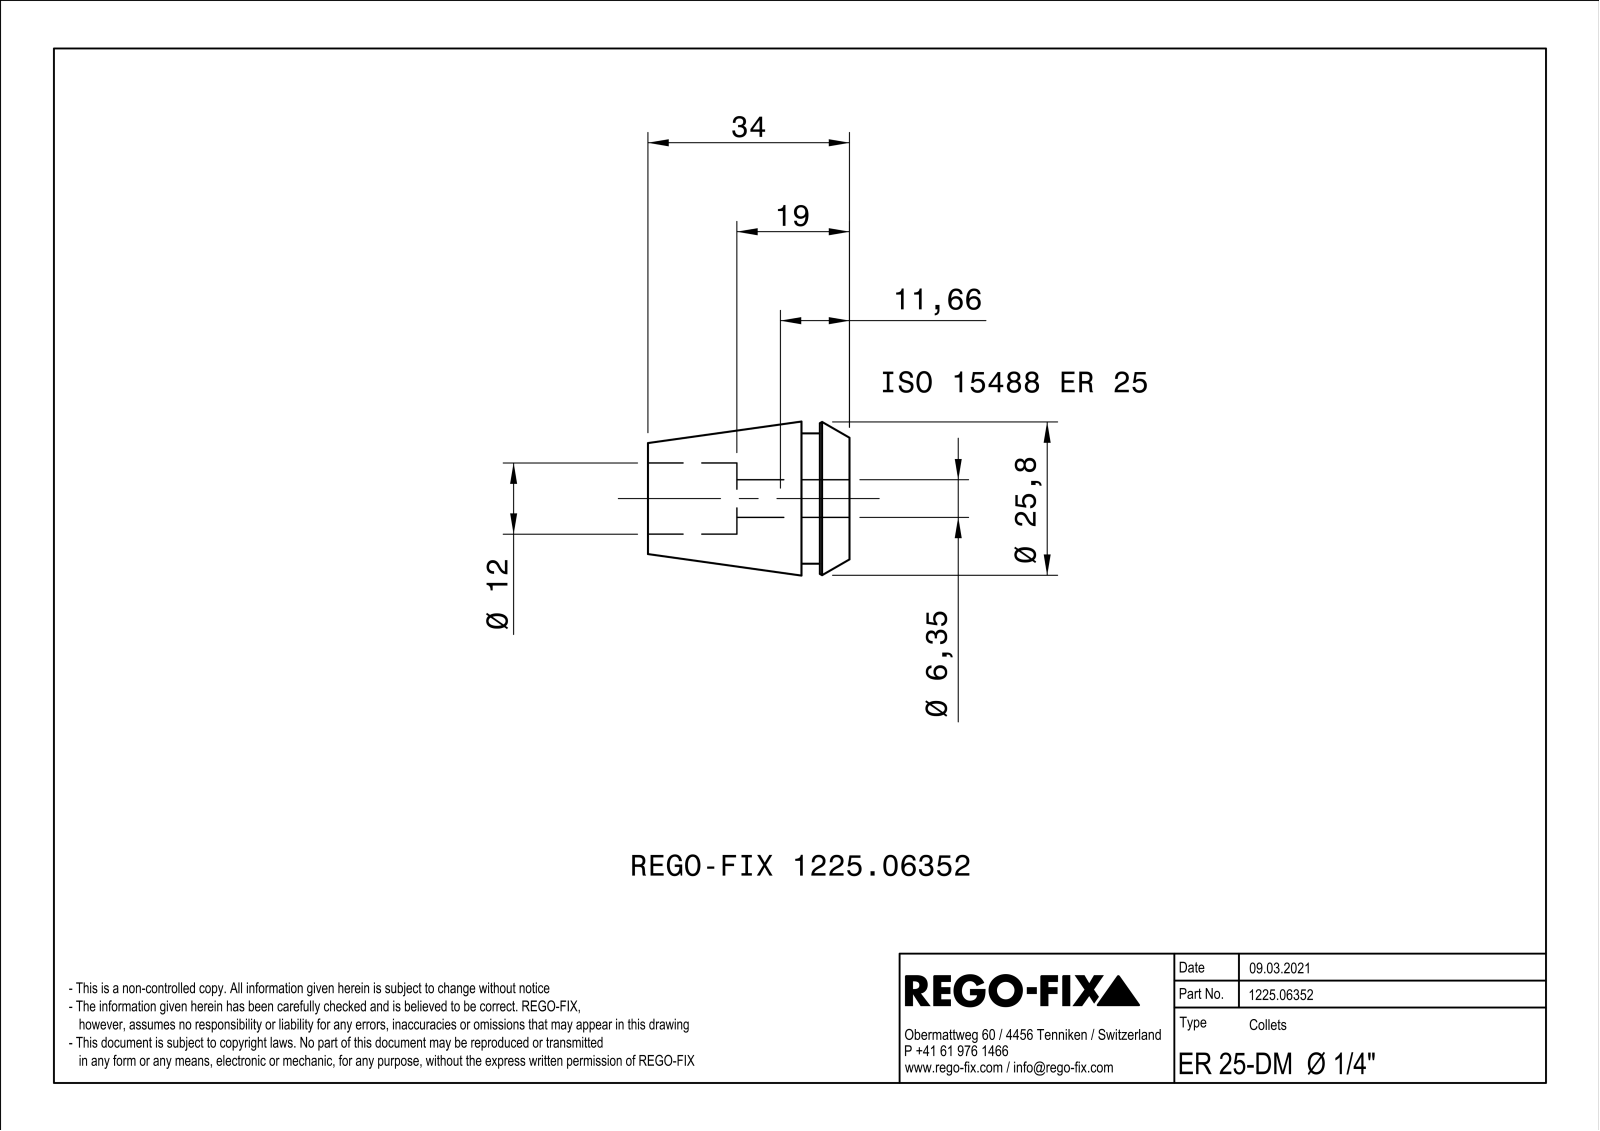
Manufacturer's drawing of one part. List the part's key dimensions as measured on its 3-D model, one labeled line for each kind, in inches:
Part name (STEP PRODUCT): NOCUT
STEP written by: SIEMENS PLM Software Solid Edge ST10 (AUTOMOTIVE_DESIGN)
Units: inches
Bodies: 1 solid, 94 faces (44 planar, 9 cylindrical, 41 other)
Overall size (bounding box): 1.339 × 1.018 × 1.018
Volume: 0.596 in³ · Surface area: 9.226 in²
Round holes (diameter × count): ⌀0.25 ×1, ⌀0.472 ×1
Round bosses / shafts (diameter × count): ⌀0.866 ×1
Main face-to-face distances: 0.024, 0.197, 0.319, 0.122, 1.339, 1.142, 1.02, 0.748, 0.551, 0.429
